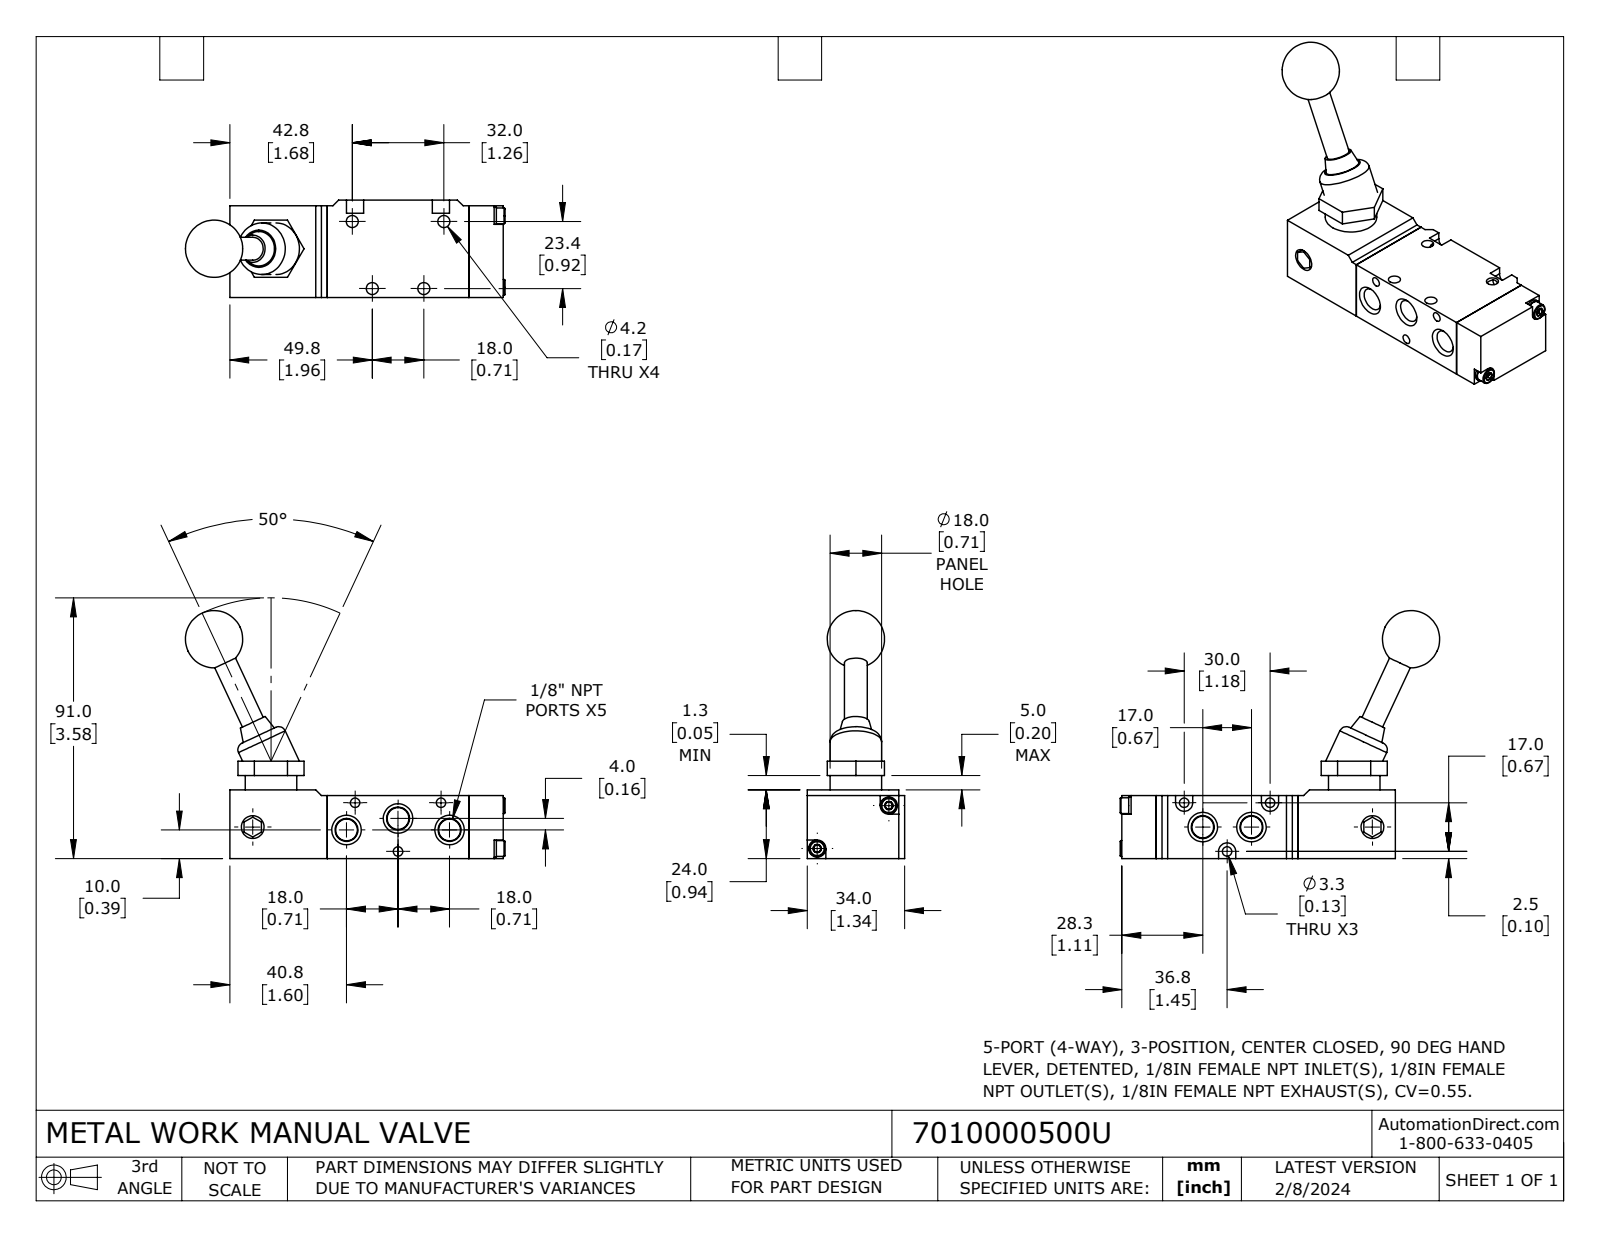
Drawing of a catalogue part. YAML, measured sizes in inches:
part_name: "7010000500U"
step_written_by: "SolidWorks 2023 (CONFIG_CONTROL_DESIGN)"
units: inches
bodies: {solids: 8, faces: 208, planar: 105, cylindrical: 49, other: 54}
overall_size: [4.393, 3.409, 1.339]
volume: 4.828
surface_area: 34.88
round_holes:
  - {diameter: 0.165, count: 4}
  - {diameter: 0.13, count: 3}
  - {diameter: 0.118, count: 2}
  - {diameter: 0.313, count: 1}
round_bosses_or_shafts:
  - {diameter: 0.709, count: 2}
  - {diameter: 0.236, count: 2}
  - {diameter: 0.217, count: 2}
  - {diameter: 0.315, count: 1}
partial_cylinders:
  - {radius: 0.118, count: 3}
face_to_face_distances: [0.866, 1.339, 1.949, 0.079, 1.26, 0.472, 3.287, 0.945, 2.421, 3.76]
hole_center_spacings: [0.893, 0.961, 1.348, 0.709, 1.148, 1.181, 1.26, 1.447]
